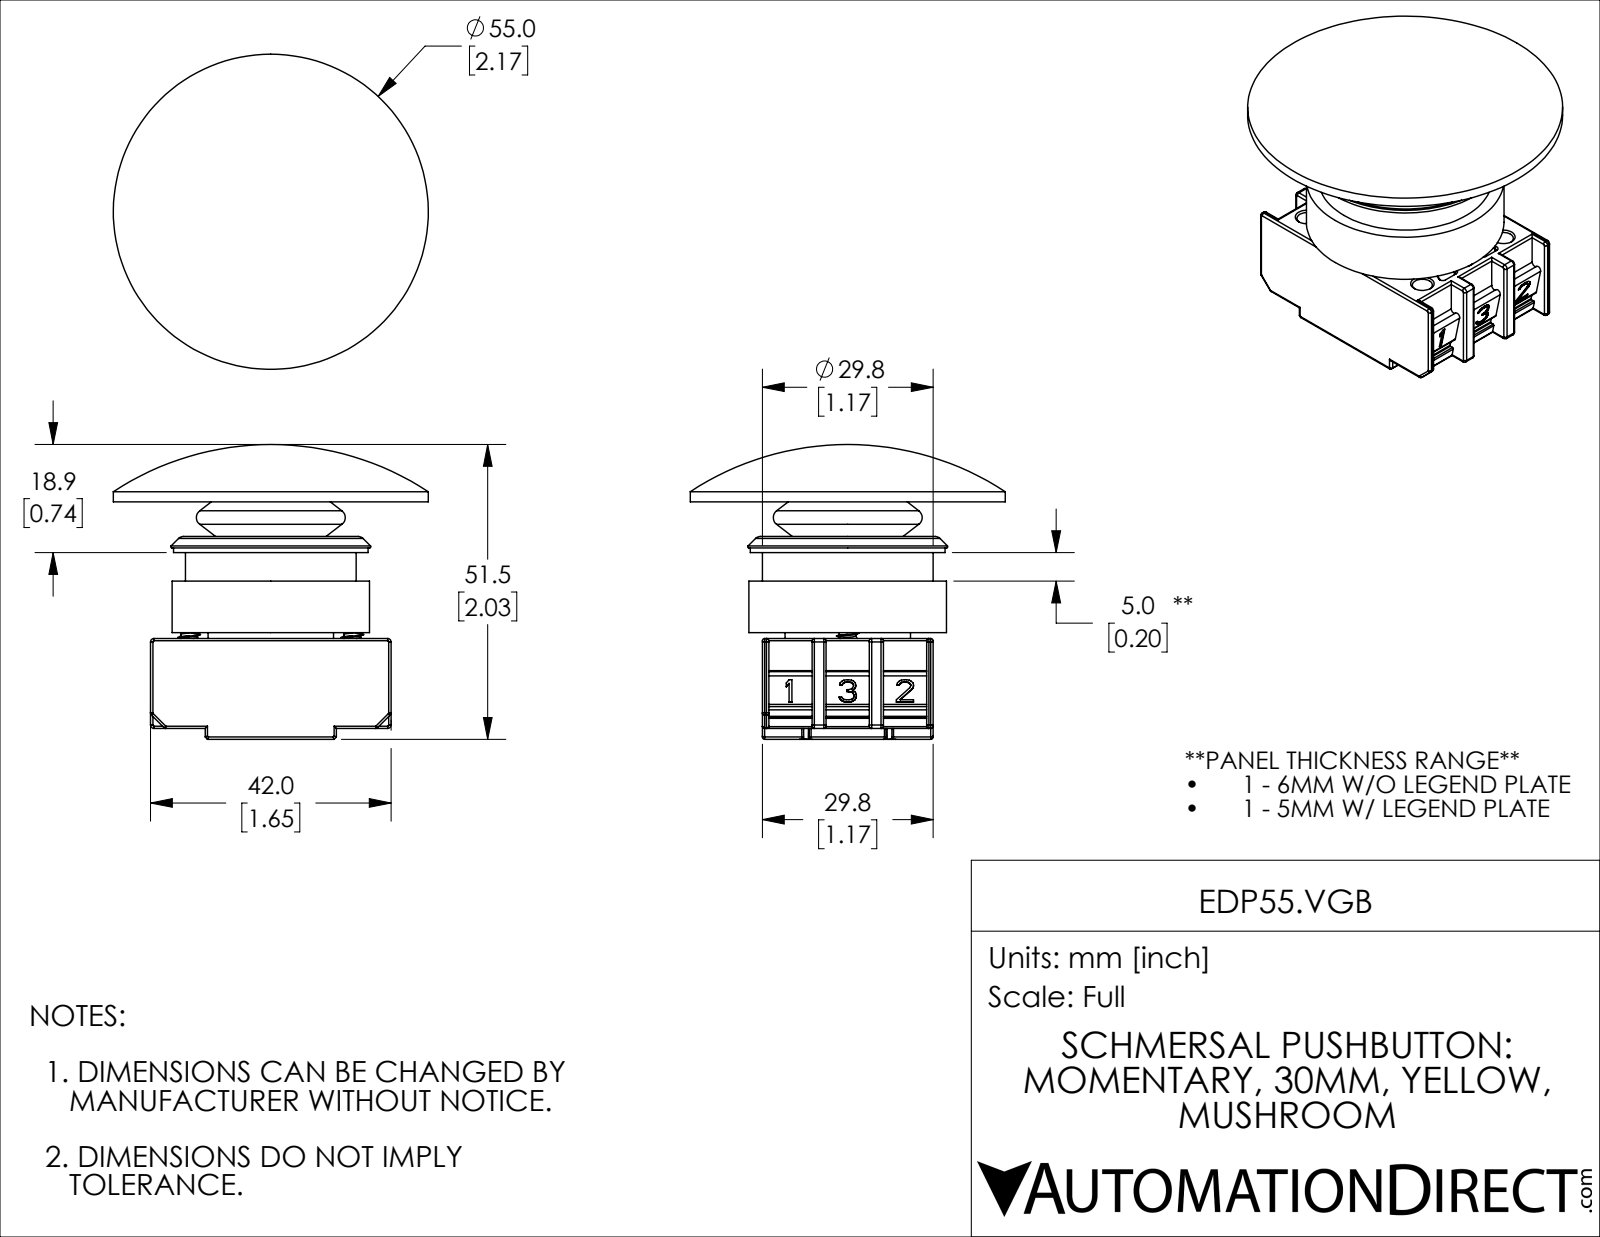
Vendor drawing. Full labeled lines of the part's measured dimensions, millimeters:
Part name (STEP PRODUCT): EDP55.VGB
STEP written by: SolidWorks 2019 (CONFIG_CONTROL_DESIGN)
Units: millimetres
Bodies: 5 solids, 1491 faces (538 planar, 502 cylindrical, 451 other)
Overall size (bounding box): 55 × 55 × 51.45
Volume: 39 129 mm³ · Surface area: 26 353 mm²
Round holes (diameter × count): ⌀3.5 ×6, ⌀5.15 ×6, ⌀12.15 ×1, ⌀17 ×1, ⌀18.8 ×1, ⌀19.5 ×1, ⌀24.1 ×1, ⌀24.2 ×1, ⌀26 ×1, ⌀30.2 ×1, ⌀32 ×1
Round bosses / shafts (diameter × count): ⌀4.8 ×2, ⌀2.93 ×2, ⌀55 ×1, ⌀34.5 ×1, ⌀34 ×1, ⌀29.8 ×1, ⌀25.5 ×1, ⌀24 ×1
Partial cylindrical surfaces — rounded edges, fillets, slot ends (radius × count): R0.4 ×112, R0.3 ×48, R0.2 ×28, R0.6 ×8, R0.5 ×6, R0.8 ×6, R0.1 ×2, R0.6 ×2
Main face-to-face distances: 18.6, 29.8, 1, 41.45, 17.6, 22.85, 1.9, 16.8, 23.85, 35.4
Hole centre spacings: 10, 17.41, 30.2, 28.5, 14.25, 20, 34.82
